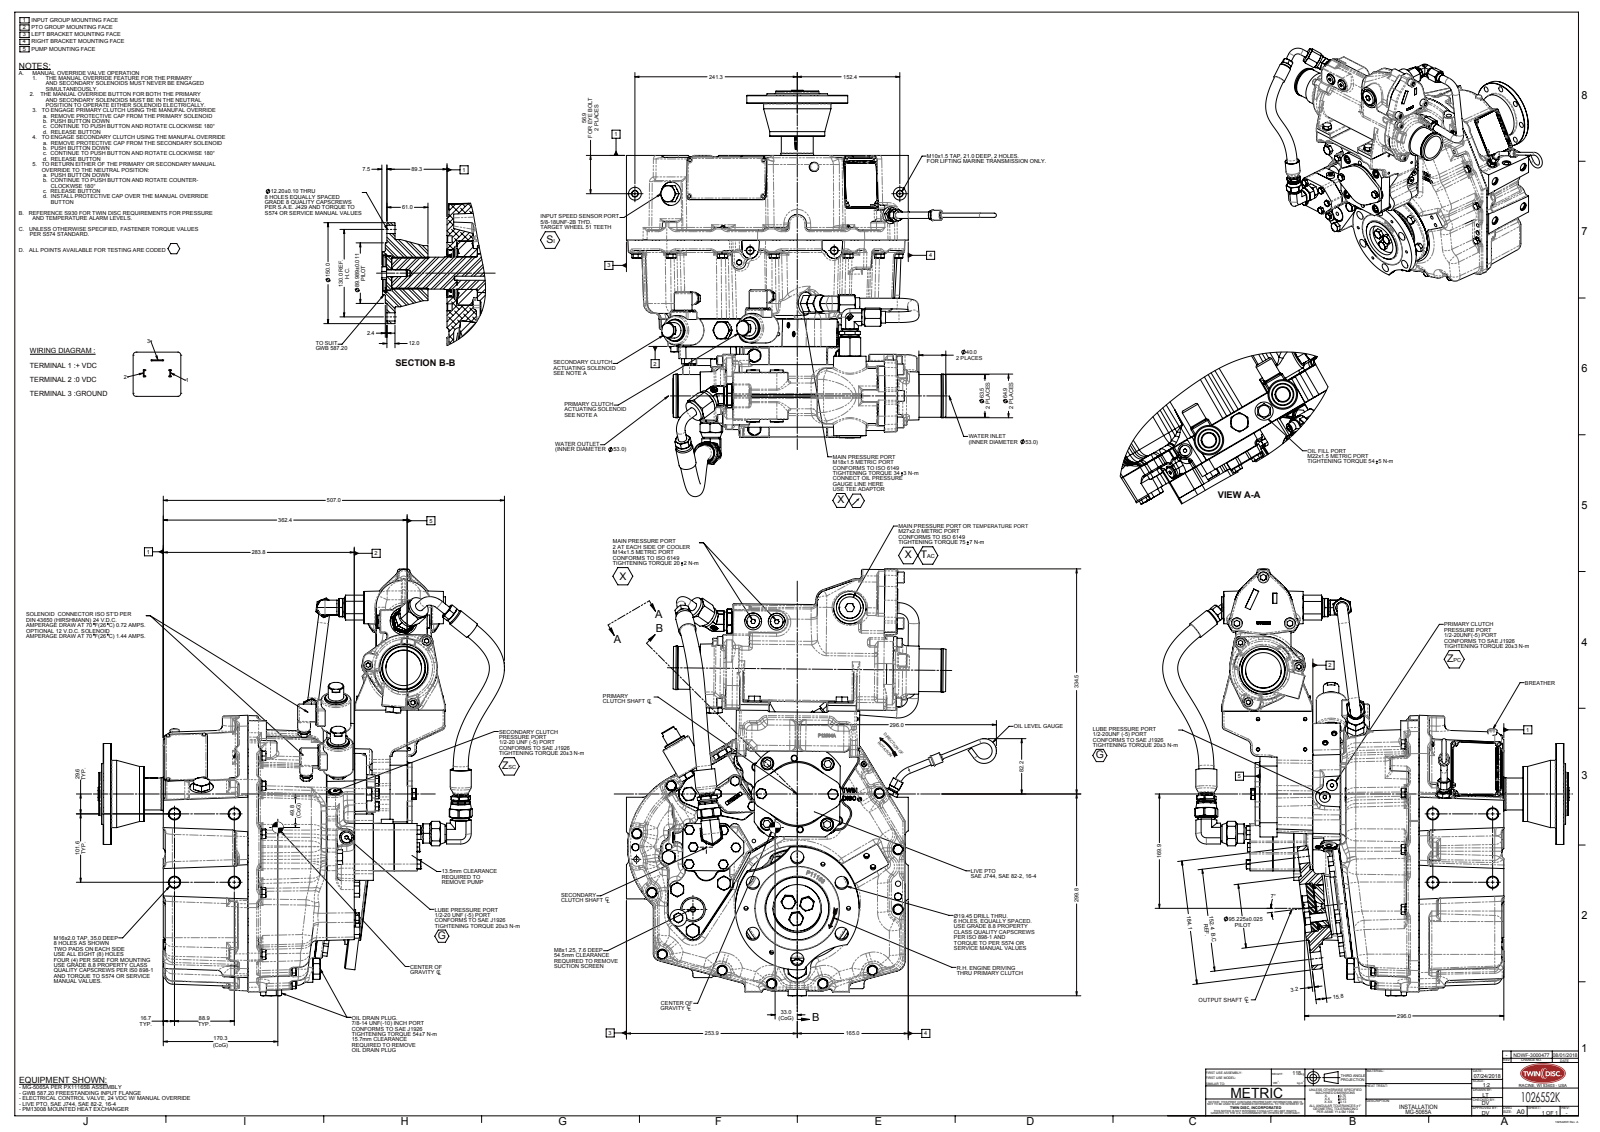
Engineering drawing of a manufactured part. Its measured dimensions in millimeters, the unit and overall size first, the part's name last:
Units: millimetres
Overall size (bounding box): 634.32 × 603.89 × 549.84
Round holes (diameter × count): ⌀10 ×15, ⌀8 ×10, ⌀12.2 ×8, ⌀19.45 ×6, ⌀6 ×4, ⌀7 ×4, ⌀12 ×4, ⌀18.13 ×4, ⌀19.05 ×4, ⌀5 ×3, ⌀12.7 ×3, ⌀5.33 ×2
Round bosses / shafts (diameter × count): ⌀15.88 ×13, ⌀13 ×7, ⌀19.85 ×4, ⌀19 ×4, ⌀15.87 ×4, ⌀16 ×3, ⌀15.9 ×3, ⌀162.56 ×2
Partial cylindrical surfaces — rounded edges, fillets, slot ends (radius × count): R4 ×79, R1 ×67, R8 ×51, R3.05 ×50, R2.5 ×47, R2 ×44, R7.62 ×32, R15.24 ×24
Main face-to-face distances: 123.42, 0.42, 123, 116.95, 117.37, 240.37, 0.79, 116.16, 116.58, 239.58
Hole centre spacings: 76.2, 49.75, 65, 76.21, 91.92, 120.1, 33.67, 49.76
Bodies: 0 solids, 4351 faces (1239 planar, 1136 cylindrical, 1976 other)
Part name (STEP PRODUCT): 1026552K
STEP written by: SolidWorks 2015 (AUTOMOTIVE_DESIGN)
